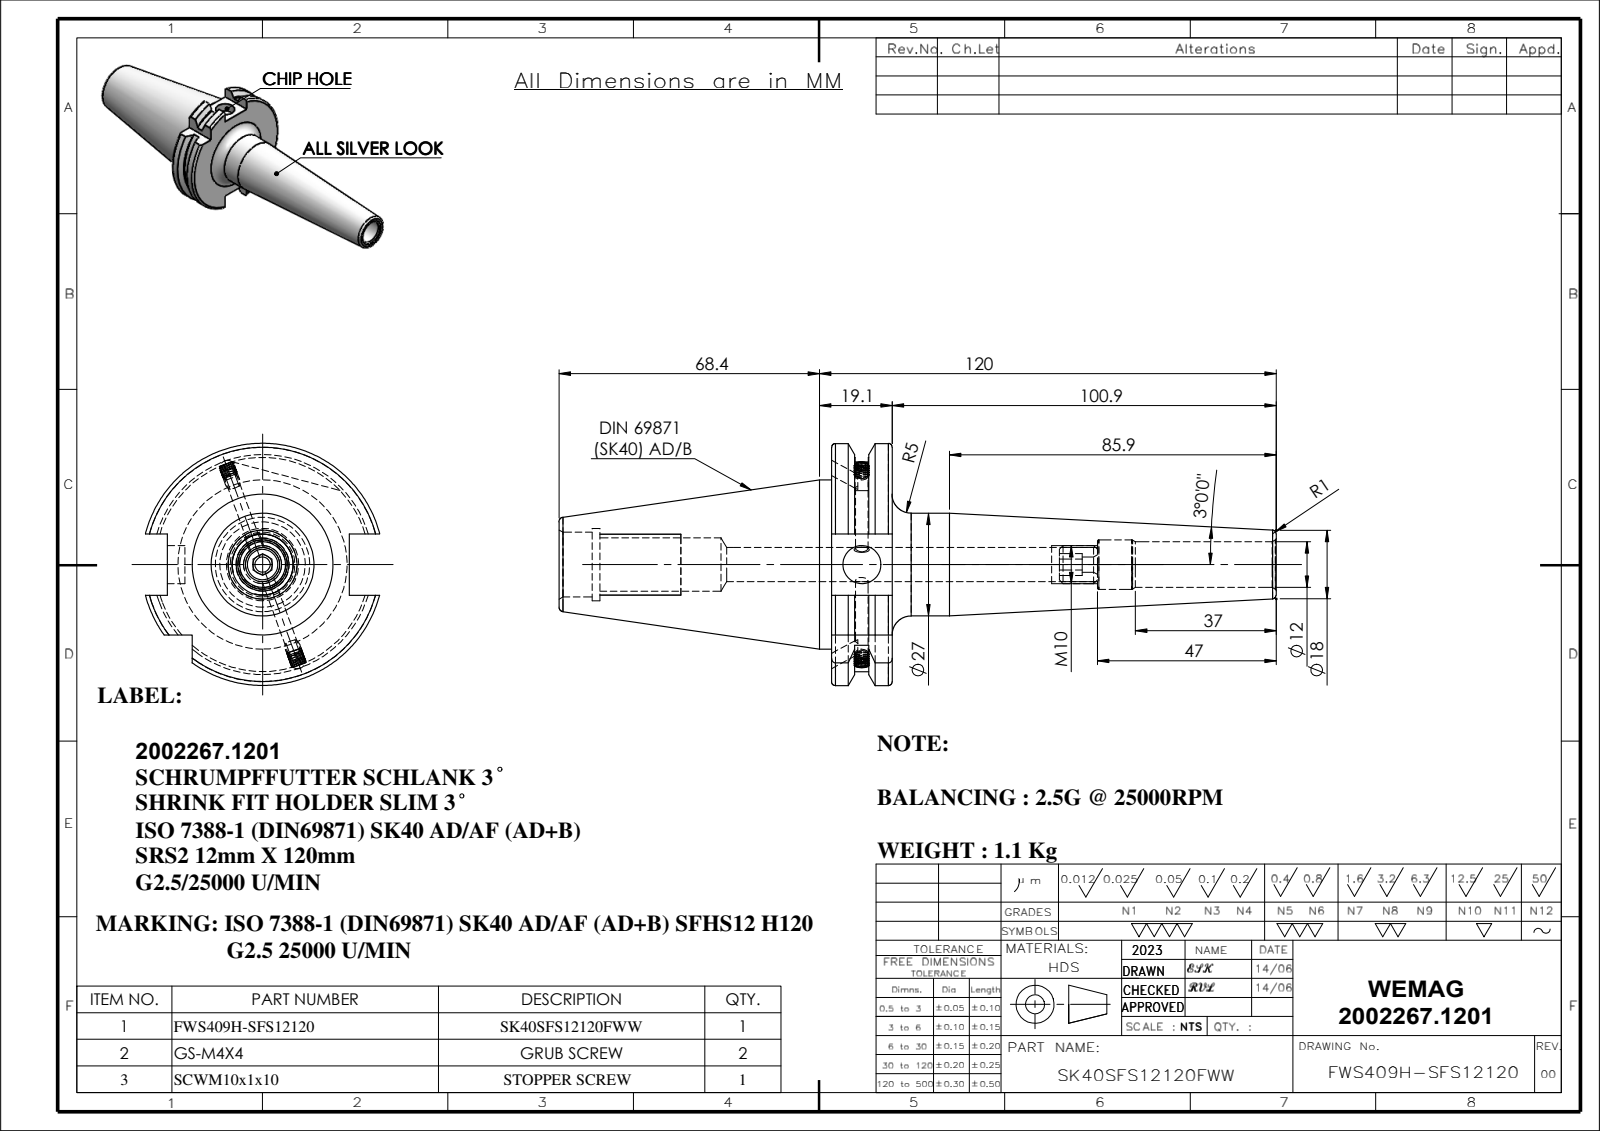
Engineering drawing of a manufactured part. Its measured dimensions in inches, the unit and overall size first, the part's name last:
Units: inches
Overall size (bounding box): 7.417 × 2.502 × 2.42
Round holes (diameter × count): ⌀0.13 ×1, ⌀0.157 ×1, ⌀0.354 ×1, ⌀0.394 ×1, ⌀0.472 ×1, ⌀0.512 ×1, ⌀0.551 ×1, ⌀0.669 ×1, ⌀0.748 ×1
Round bosses / shafts (diameter × count): ⌀0.157 ×2, ⌀1.75 ×1, ⌀1.063 ×1, ⌀0.394 ×1
Partial cylindrical surfaces — rounded edges, fillets, slot ends (radius × count): R1.107 ×1, R1.251 ×1
Main face-to-face distances: 0.626, 0.634, 1.882, 2.819, 3.445, 0.421, 2.398, 3.024, 3.056, 2.635
Volume: 8.399 in³ · Surface area: 49.1 in²
Bodies: 4 solids, 220 faces (56 planar, 58 cylindrical, 106 other)
Part name (STEP PRODUCT): SK40SFS12120FWW; GS-M4X4_DIN 913 - M4 x 4-N; SCWM10X1-10; 91406-SRS212120
STEP written by: SolidWorks 2018 (CONFIG_CONTROL_DESIGN)
